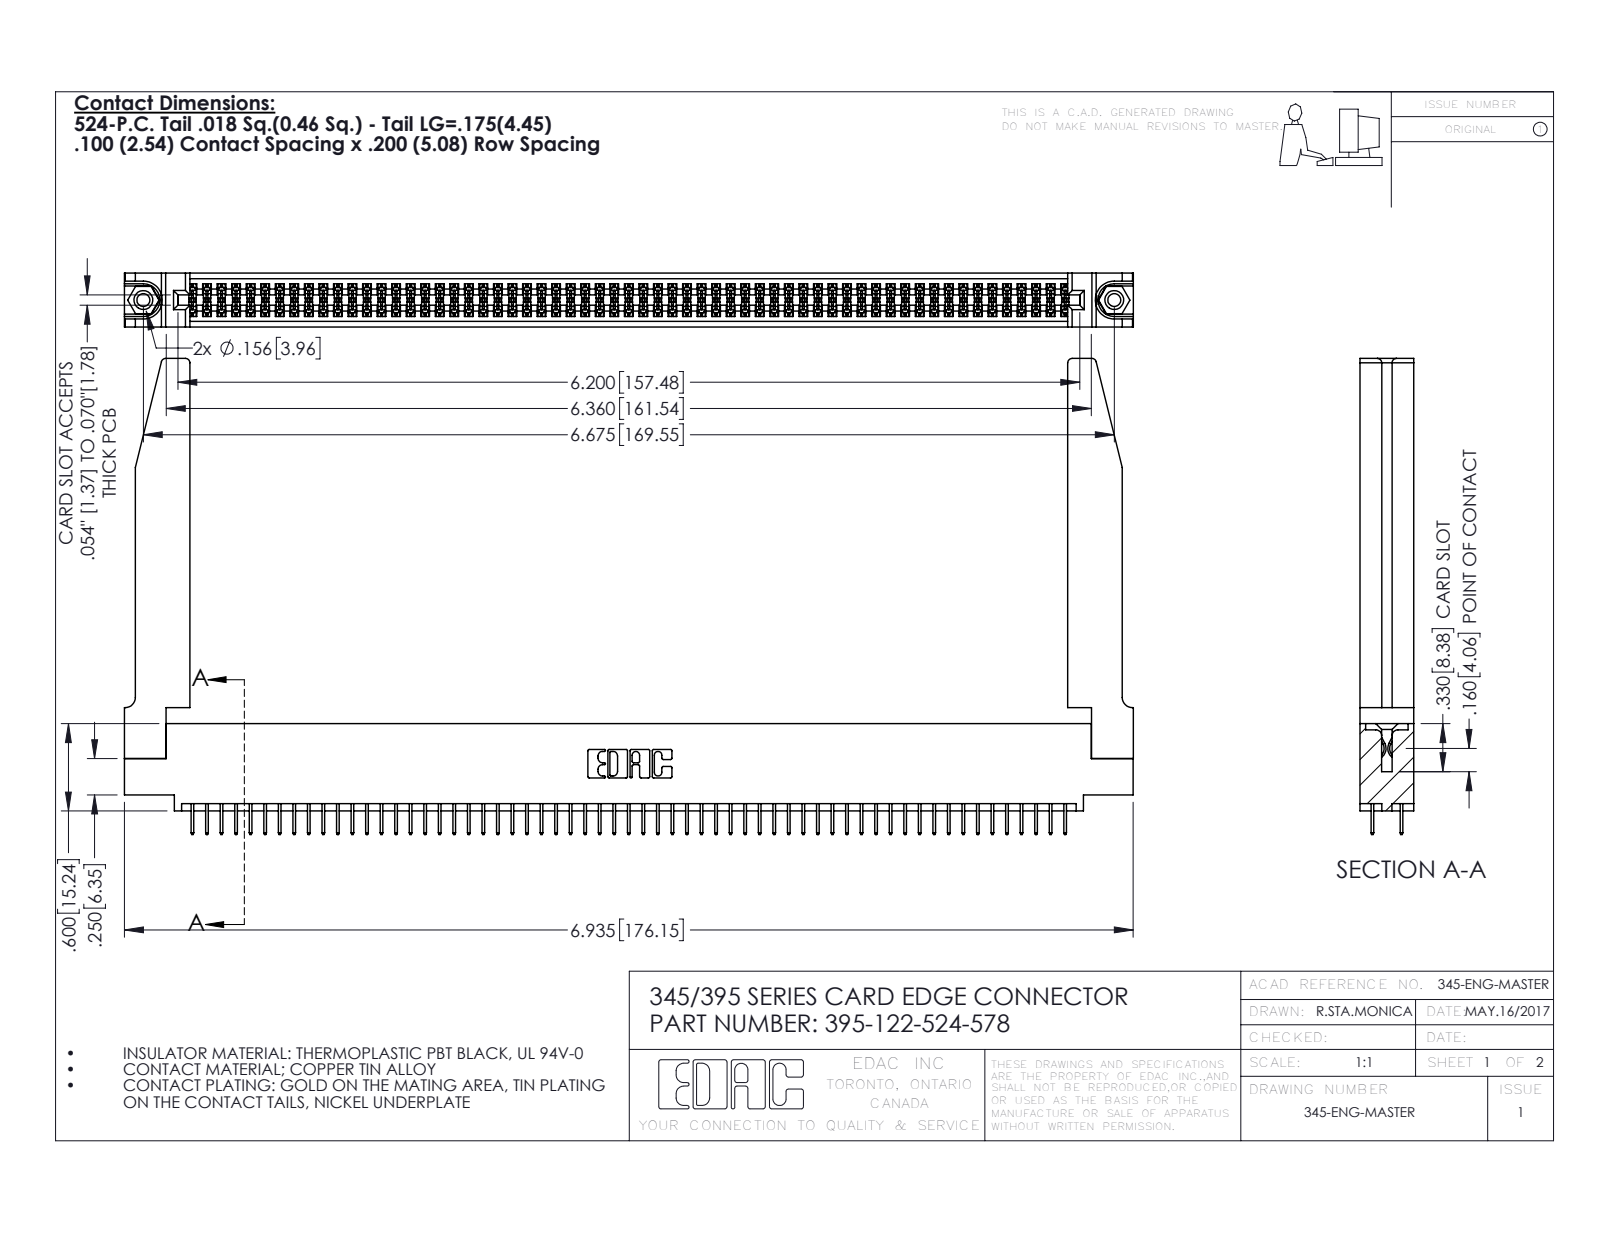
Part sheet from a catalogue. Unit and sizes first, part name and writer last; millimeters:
Units: millimetres
Overall size (bounding box): 176.2 × 83.1 × 9.4
Round holes (diameter × count): ⌀2.3 ×2, ⌀3.2 ×2, ⌀4 ×2, ⌀1.6 ×1
Round bosses / shafts (diameter × count): ⌀3.9 ×2
Partial cylindrical surfaces — rounded edges, fillets, slot ends (radius × count): R0.2 ×183, R0.3 ×22, R0.8 ×8, R0.2 ×6, R0.8 ×6, R0.7 ×3, R0.4 ×2, R0.5 ×2
Main face-to-face distances: 1.8, 9.4, 7.6, 5.1, 2.5, 6.9, 0.6, 5.7, 1.8, 4.4
Hole centre spacings: 6.9, 163.6, 169.5
Volume: 24 810 mm³ · Surface area: 31 990 mm²
Bodies: 127 solids, 6952 faces (4984 planar, 1916 cylindrical, 52 other)
Part name (STEP PRODUCT): 345 Part_0.110 Offset - 0.156 Dia-TH; 395-122-524-578; 345-292-001_345-293-124; 345-250-001_345-250-001-102 (+1 more)
STEP written by: SolidWorks 2016 (CONFIG_CONTROL_DESIGN)
